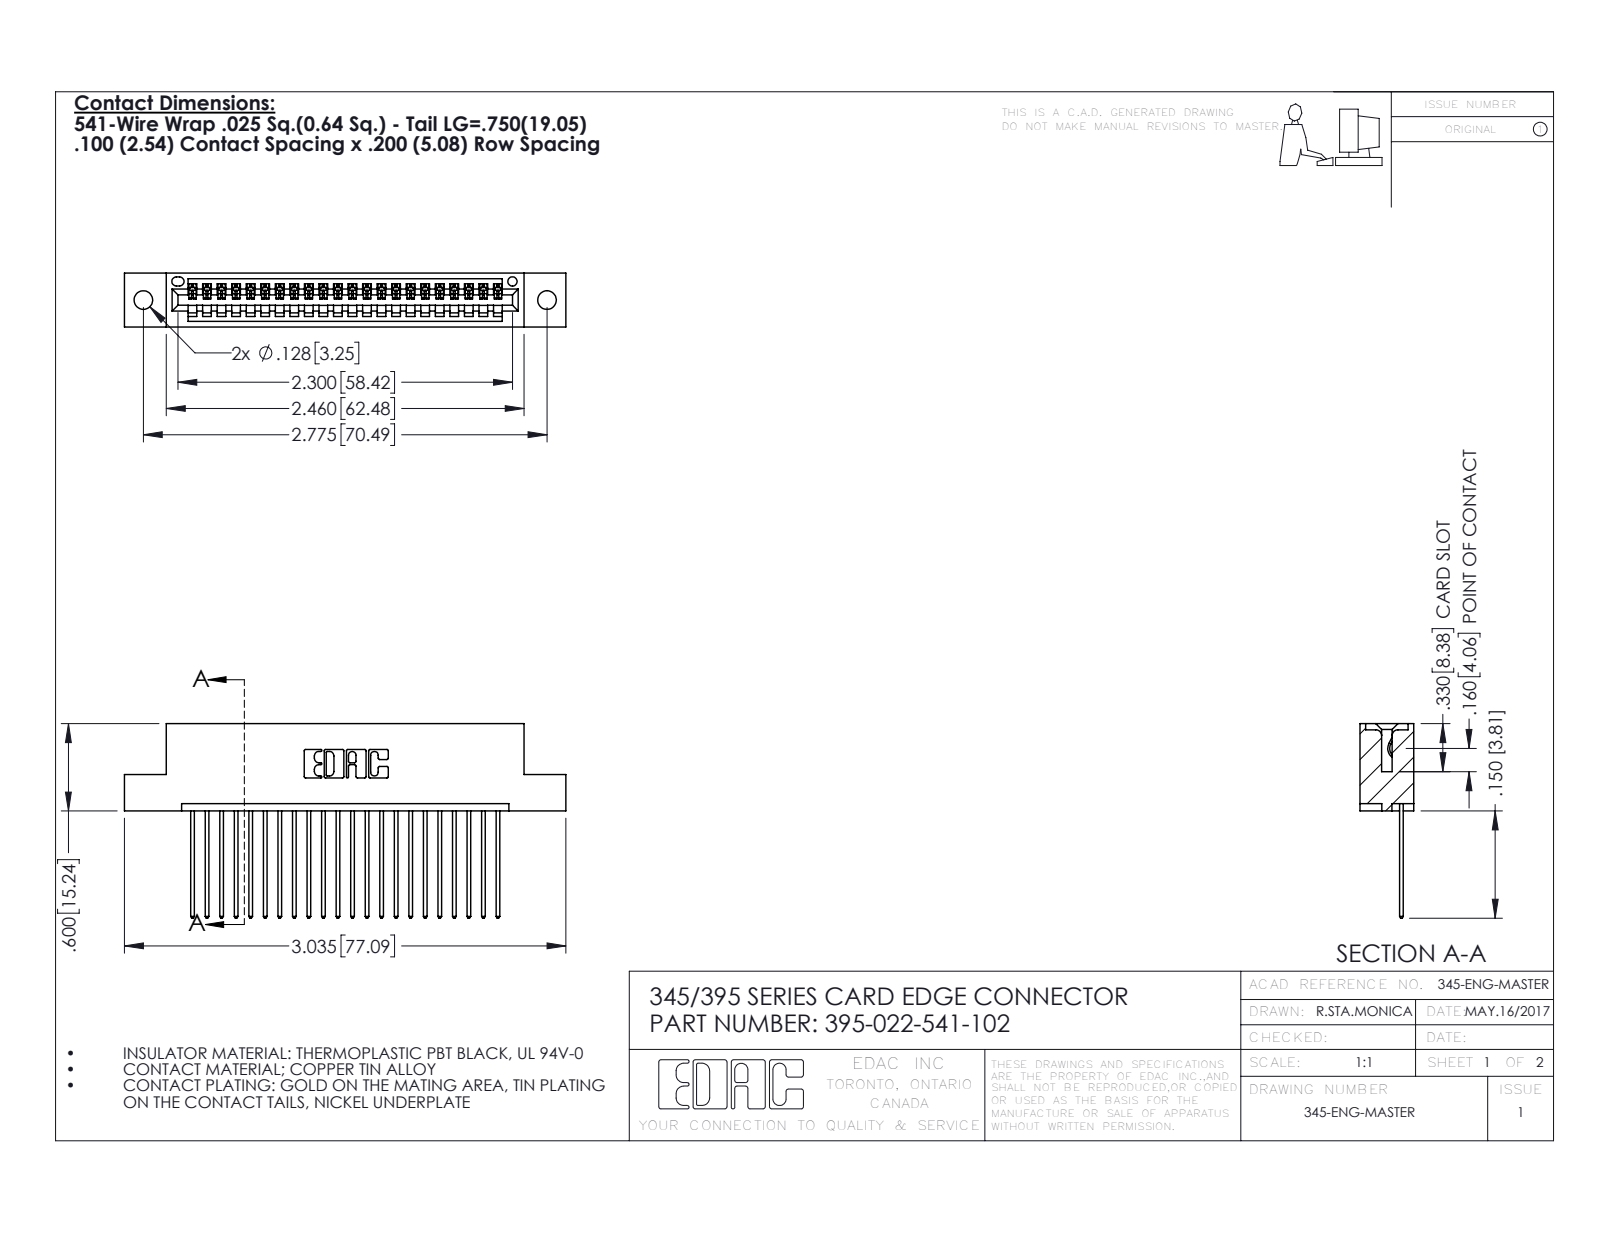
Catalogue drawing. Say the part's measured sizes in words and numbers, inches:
The part is named "345 Part_Flush Mounting Lugs - 0.128 Dia; 345-292-001_345-293-141; 395-022-541-102". Its 3-D file was written by "SolidWorks 2016 (CONFIG_CONTROL_DESIGN)". It is 23 solids with 1402 faces: 960 planar, 442 cylindrical and 0 other. Overall it measures 3.035 by 1.337 by 0.37 inches. Its volume is 0.439 cubic inches and its surface area 14.64 square inches. Round holes: 2 of diameter 0.128, 1 of diameter 0.064. Partial cylindrical surfaces (rounded edges, fillets, slot ends): 44 of radius 0.006, 44 of radius 0.01, 22 of radius 0.01, 6 of radius 0.007, 6 of radius 0.031, 3 of radius 0.026, 2 of radius 0.031, 2 of radius 0.04. The main face-to-face distances are 0.298, 0.072, 0.2, 0.37, 0.098, 0.272, 0.025, 0.225, 0.149, 0.072. The hole center spacings are 0.27, 2.541, 2.775.
